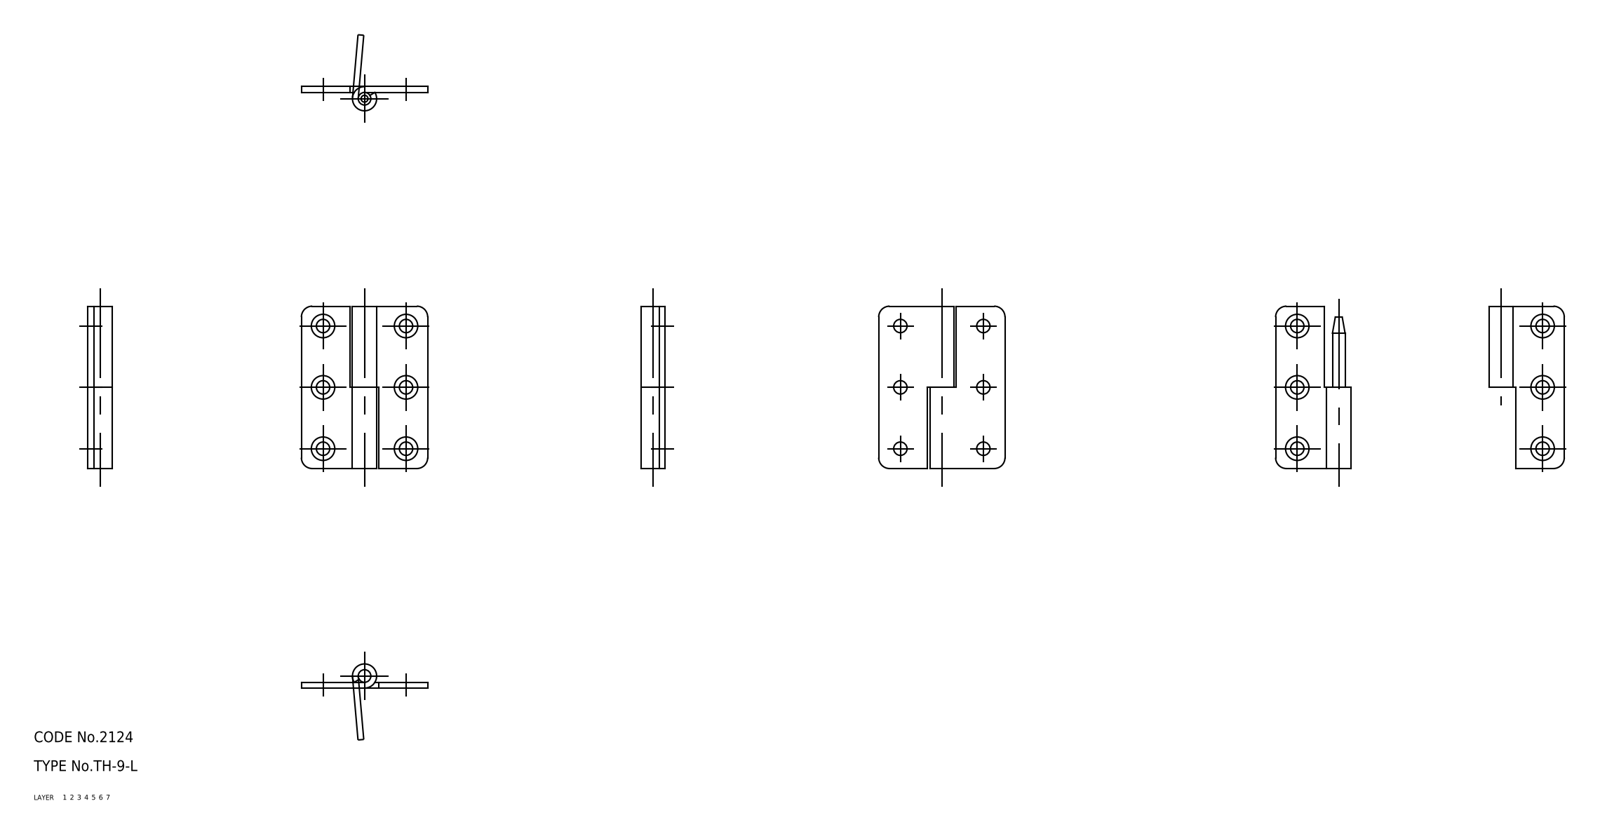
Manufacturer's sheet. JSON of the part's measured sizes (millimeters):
{"part_name": "shaft; hinge piece_B; hinge piece_A; TH_9_L_19933_36", "step_written_by": "CADfix (AUTOMOTIVE_DESIGN)", "units": "millimeters", "bodies": {"solids": 3, "faces": 54, "planar": 0, "cylindrical": 0, "other": 54}, "overall_size": [45, 35, 6.7], "volume_mm3": 3382, "surface_area_mm2": 4860}
